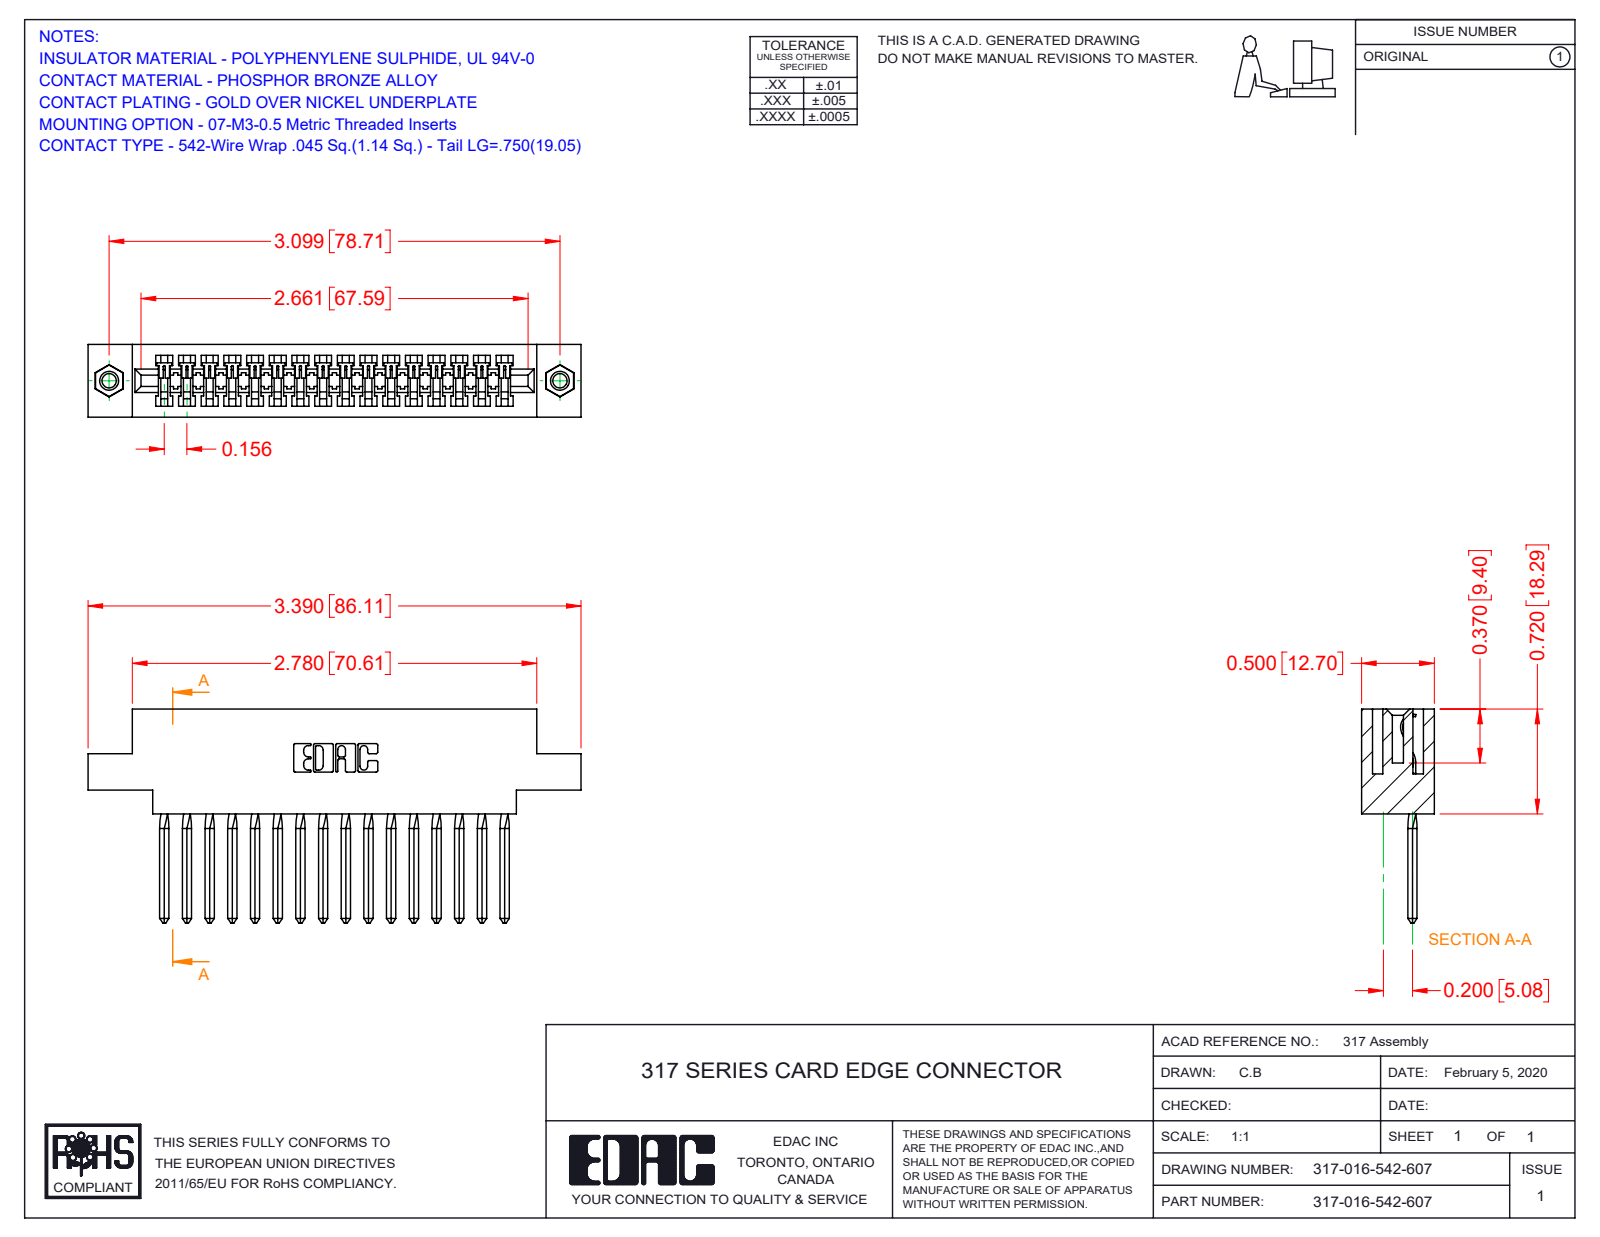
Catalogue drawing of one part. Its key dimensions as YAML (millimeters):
part_name: "317-290-003_542; 317-016-542-607; 345-250-001_345-250-005-103; 317 Part_.156 Dia - TI"
step_written_by: "SolidWorks 2016 (CONFIG_CONTROL_DESIGN)"
units: millimeters
bodies: {solids: 19, faces: 1362, planar: 1114, cylindrical: 168, other: 80}
overall_size: [86.1, 37.3, 12.7]
volume: 12600
surface_area: 14820
round_holes:
  - {diameter: 2.5, count: 2}
  - {diameter: 3.2, count: 2}
  - {diameter: 4, count: 2}
round_bosses_or_shafts:
  - {diameter: 3.9, count: 2}
partial_cylinders:
  - {radius: 0.2, count: 32}
  - {radius: 0.3, count: 22}
  - {radius: 0.2, count: 6}
  - {radius: 0.8, count: 6}
  - {radius: 0.7, count: 3}
  - {radius: 1.9, count: 1}
  - {radius: 2.3, count: 1}
  - {radius: 2.5, count: 1}
face_to_face_distances: [12.7, 1.9, 10.8, 2.8, 8.9, 1.7, 3.5, 5.6, 18.3, 5.4]
hole_center_spacings: [78.7]
